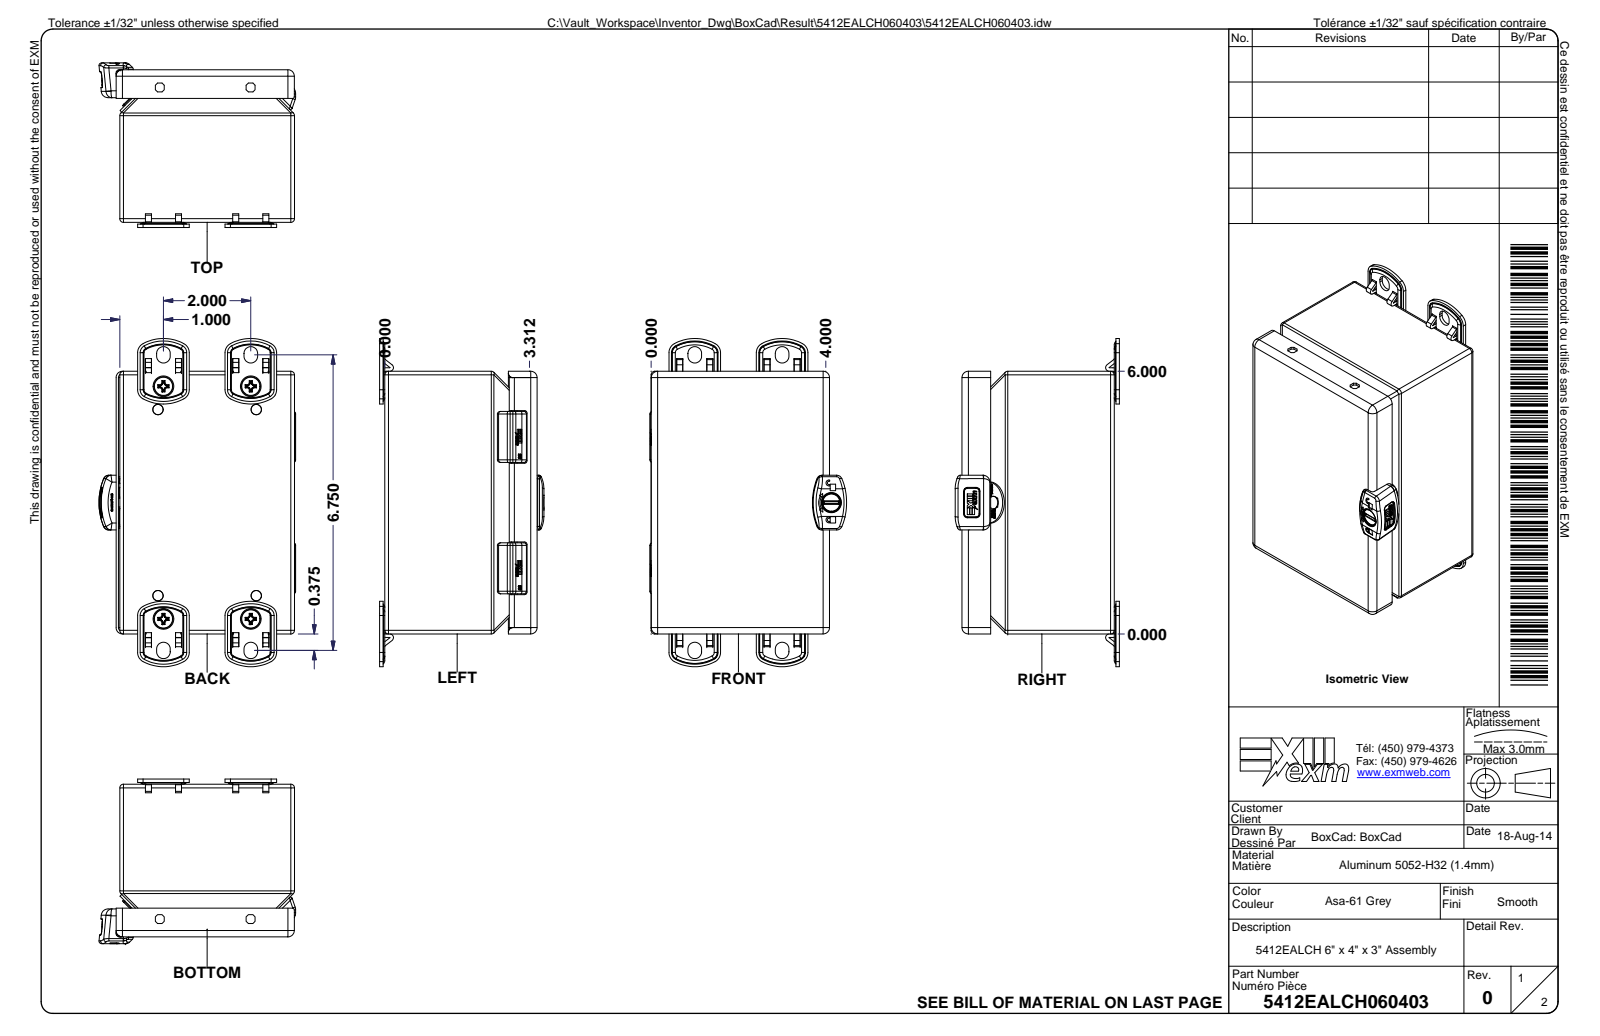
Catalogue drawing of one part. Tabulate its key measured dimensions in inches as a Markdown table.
| quantity | value |
| --- | --- |
| part name | 5412EALCH060403; 5412EALCH060403B; 5412EALCH060403B-P; STK-A-70469-1 (+8 more) |
| STEP written by | Autodesk Inventor 2020 (AUTOMOTIVE_DESIGN) |
| units | inches |
| bodies | 51 solids, 6818 faces (2990 planar, 1592 cylindrical, 2236 other) |
| overall size | 7.496 × 4.503 × 3.76 |
| volume | 10.57 in³ |
| surface area | 376.9 in² |
| round holes (diameter × count) | 0.197 × 6, 0.197 × 4, 0.236 × 4, 0.32 × 4, 0.165 × 3, 0.173 × 3, 0.236 × 3, 0.03 × 2, 0.175 × 2, 0.201 × 2, 0.24 × 2, 0.394 × 2 |
| round bosses / shafts (diameter × count) | 0.232 × 8, 0.5 × 4, 0.236 × 4, 0.3 × 3, 0.197 × 3, 0.193 × 3, 0.394 × 2, 0.035 × 2 |
| partial cylindrical surfaces (radius × count) | 0.02 × 213, 0.01 × 152, 0.039 × 86, 0.008 × 60, 0.059 × 55, 0.004 × 54, 0.031 × 33, 0.084 × 24 |
| main face-to-face distances | 0.053, 0.053, 3.947, 3.433, 3.38, 3.486, 3.433, 5.947, 0.236, 0.304 |
| hole center spacings | 0.546, 4.782, 4.809, 4.25, 2.19, 2.25, 2.191, 2.349 |
